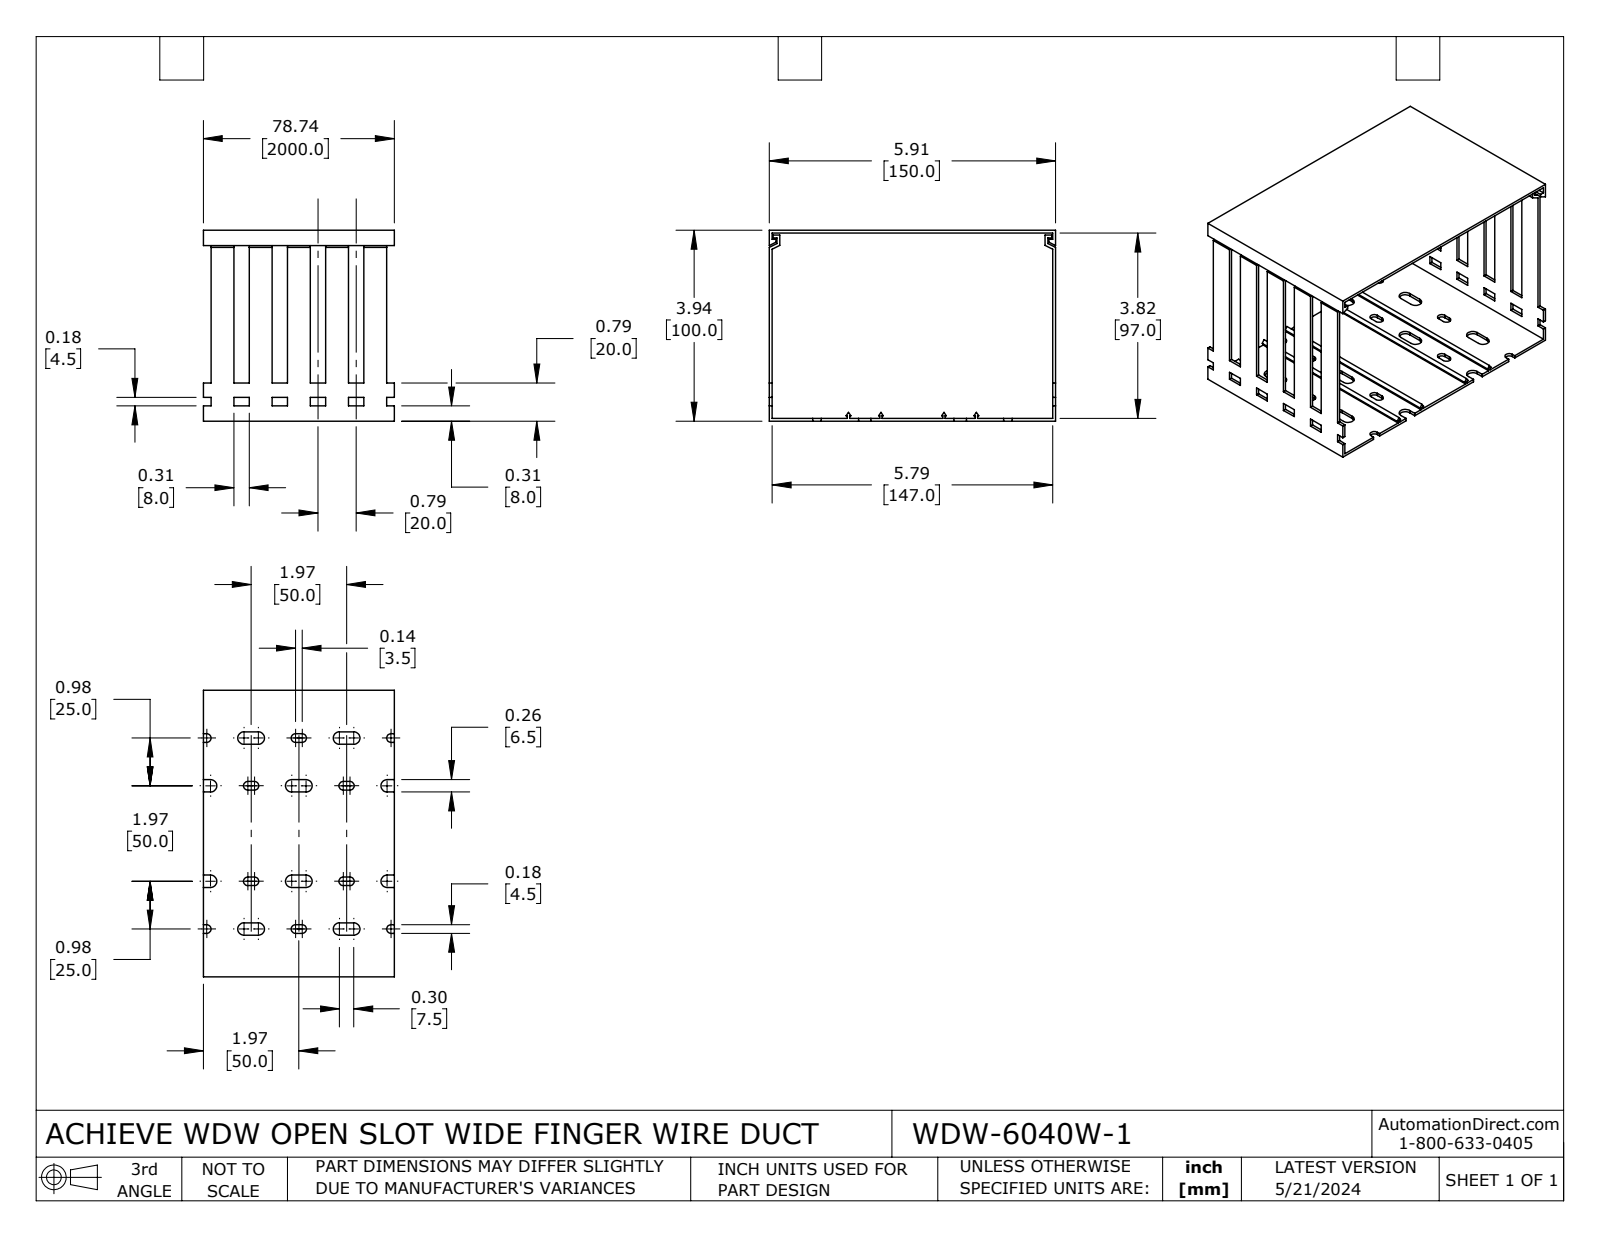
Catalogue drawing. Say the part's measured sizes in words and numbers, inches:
The part is named "WDW-6040W-1". Its 3-D file was written by "SolidWorks 2023 (CONFIG_CONTROL_DESIGN)". It is 2 solids with 280 faces: 248 planar, 32 cylindrical and 0 other. Overall it measures 5.906 by 3.937 by 3.937 inches. Its volume is 4.124 cubic inches and its surface area 148.2 square inches. Partial cylindrical surfaces (rounded edges, fillets, slot ends): 16 of radius 0.089, 16 of radius 0.128. The main face-to-face distances are 0.059, 3.878, 3.937, 3.819, 5.846, 5.906, 5.787, 0.787, 0.157, 1.575.
